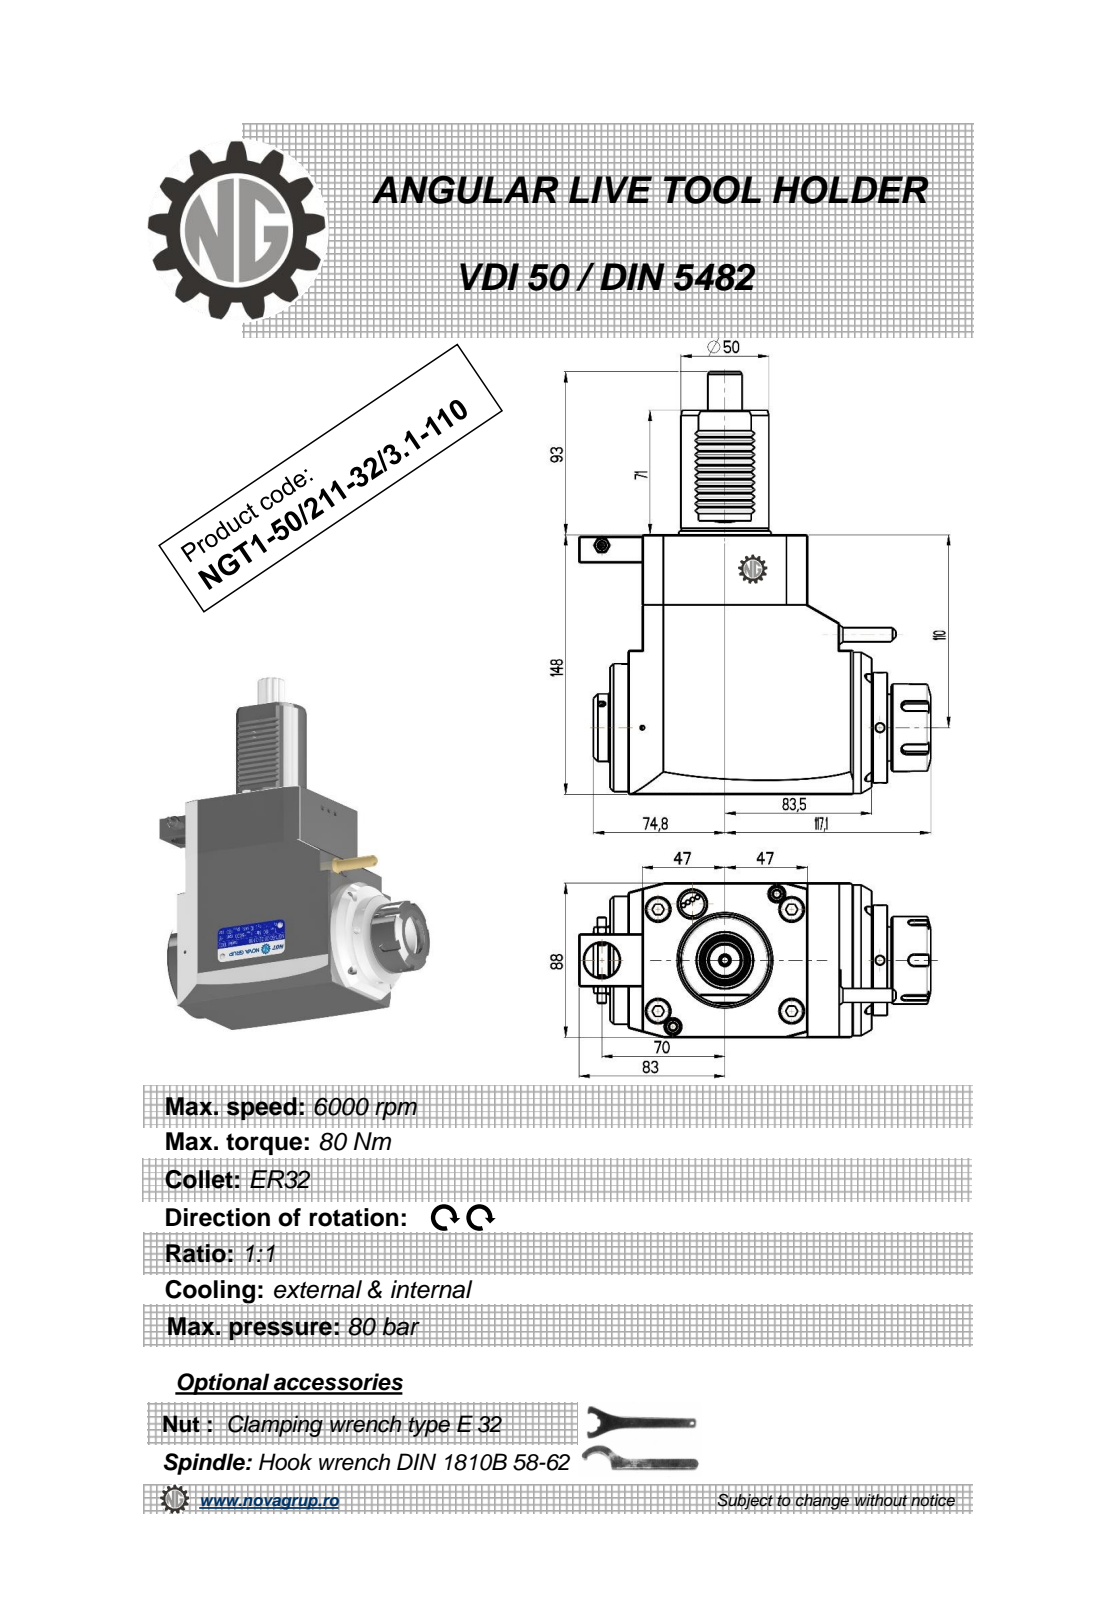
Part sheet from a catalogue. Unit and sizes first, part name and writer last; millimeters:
Units: millimetres
Overall size (bounding box): 241 × 200.1 × 88
Round holes (diameter × count): ⌀5 ×3, ⌀3 ×1, ⌀4.2 ×1, ⌀5.3 ×1, ⌀9.5 ×1, ⌀20 ×1, ⌀27 ×1
Round bosses / shafts (diameter × count): ⌀50 ×2, ⌀86 ×1, ⌀73 ×1, ⌀63 ×1, ⌀50.5 ×1, ⌀41 ×1, ⌀40 ×1, ⌀38.5 ×1
Partial cylindrical surfaces — rounded edges, fillets, slot ends (radius × count): R3.33 ×24, R0.26 ×12, R0.3 ×12, R0.2 ×6, R3 ×5, R8.25 ×1, R9.75 ×1
Main face-to-face distances: 88, 148, 8, 94, 130.5, 36.5, 120, 18.3, 112.3, 148.8
Hole centre spacings: 52.46, 56.65, 70, 88.25, 101.5, 158.25
Volume: 1 815 000 mm³ · Surface area: 113 657 mm²
Bodies: 1 solid, 475 faces (190 planar, 140 cylindrical, 145 other)
Part name (STEP PRODUCT): NGT1_50_211_32_3_1_110
STEP written by: PRO/ENGINEER BY PARAMETRIC TECHNOLOGY CORPORATION, 2010280 (CONFIG_CONTROL_DESIGN)
